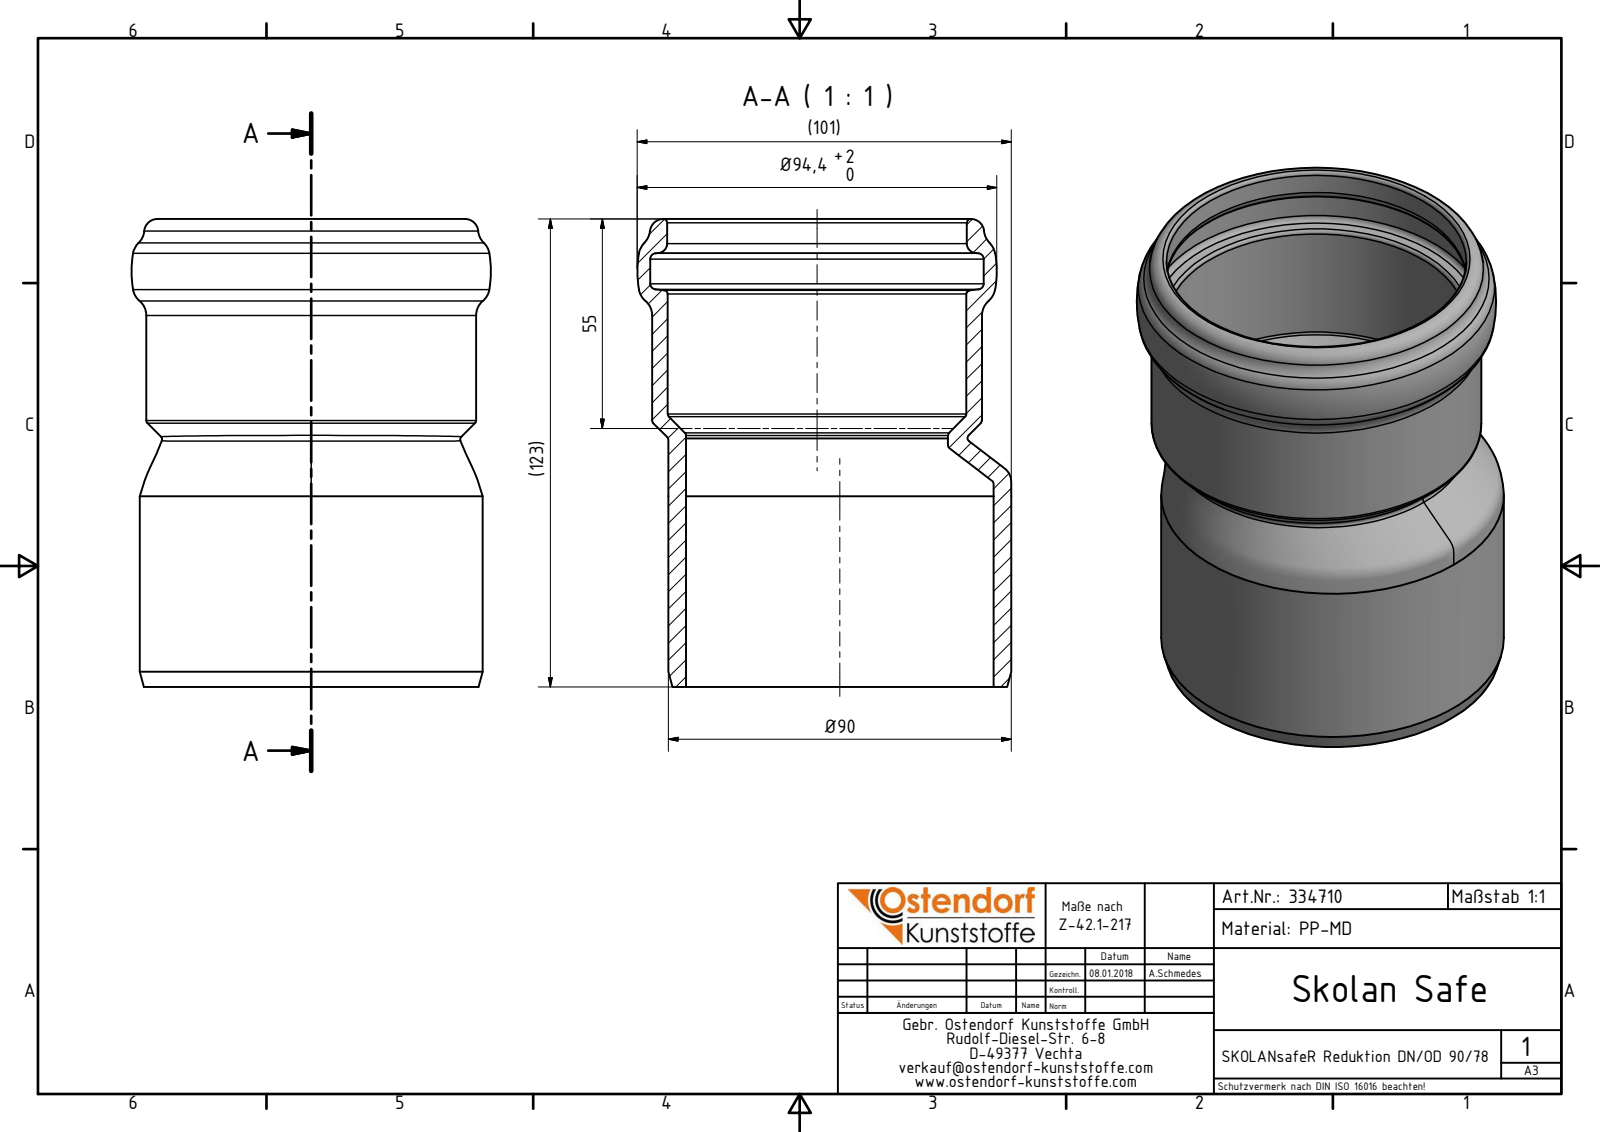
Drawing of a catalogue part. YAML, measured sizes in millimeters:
part_name: "334710 SKOLANsafeR Reduktion DN_OD 90_78"
step_written_by: "Autodesk Inventor 2016 (AUTOMOTIVE_DESIGN)"
units: millimeters
bodies: {solids: 1, faces: 30, planar: 1, cylindrical: 7, other: 22}
overall_size: [122.8, 98.2, 94.4]
volume: 147532
surface_area: 70403
round_holes:
  - {diameter: 68.8, count: 1}
  - {diameter: 78.4, count: 1}
  - {diameter: 78.7, count: 1}
  - {diameter: 80.8, count: 1}
  - {diameter: 87.6, count: 1}
round_bosses_or_shafts:
  - {diameter: 90, count: 1}
  - {diameter: 86.6, count: 1}
hole_center_spacings: [6]
